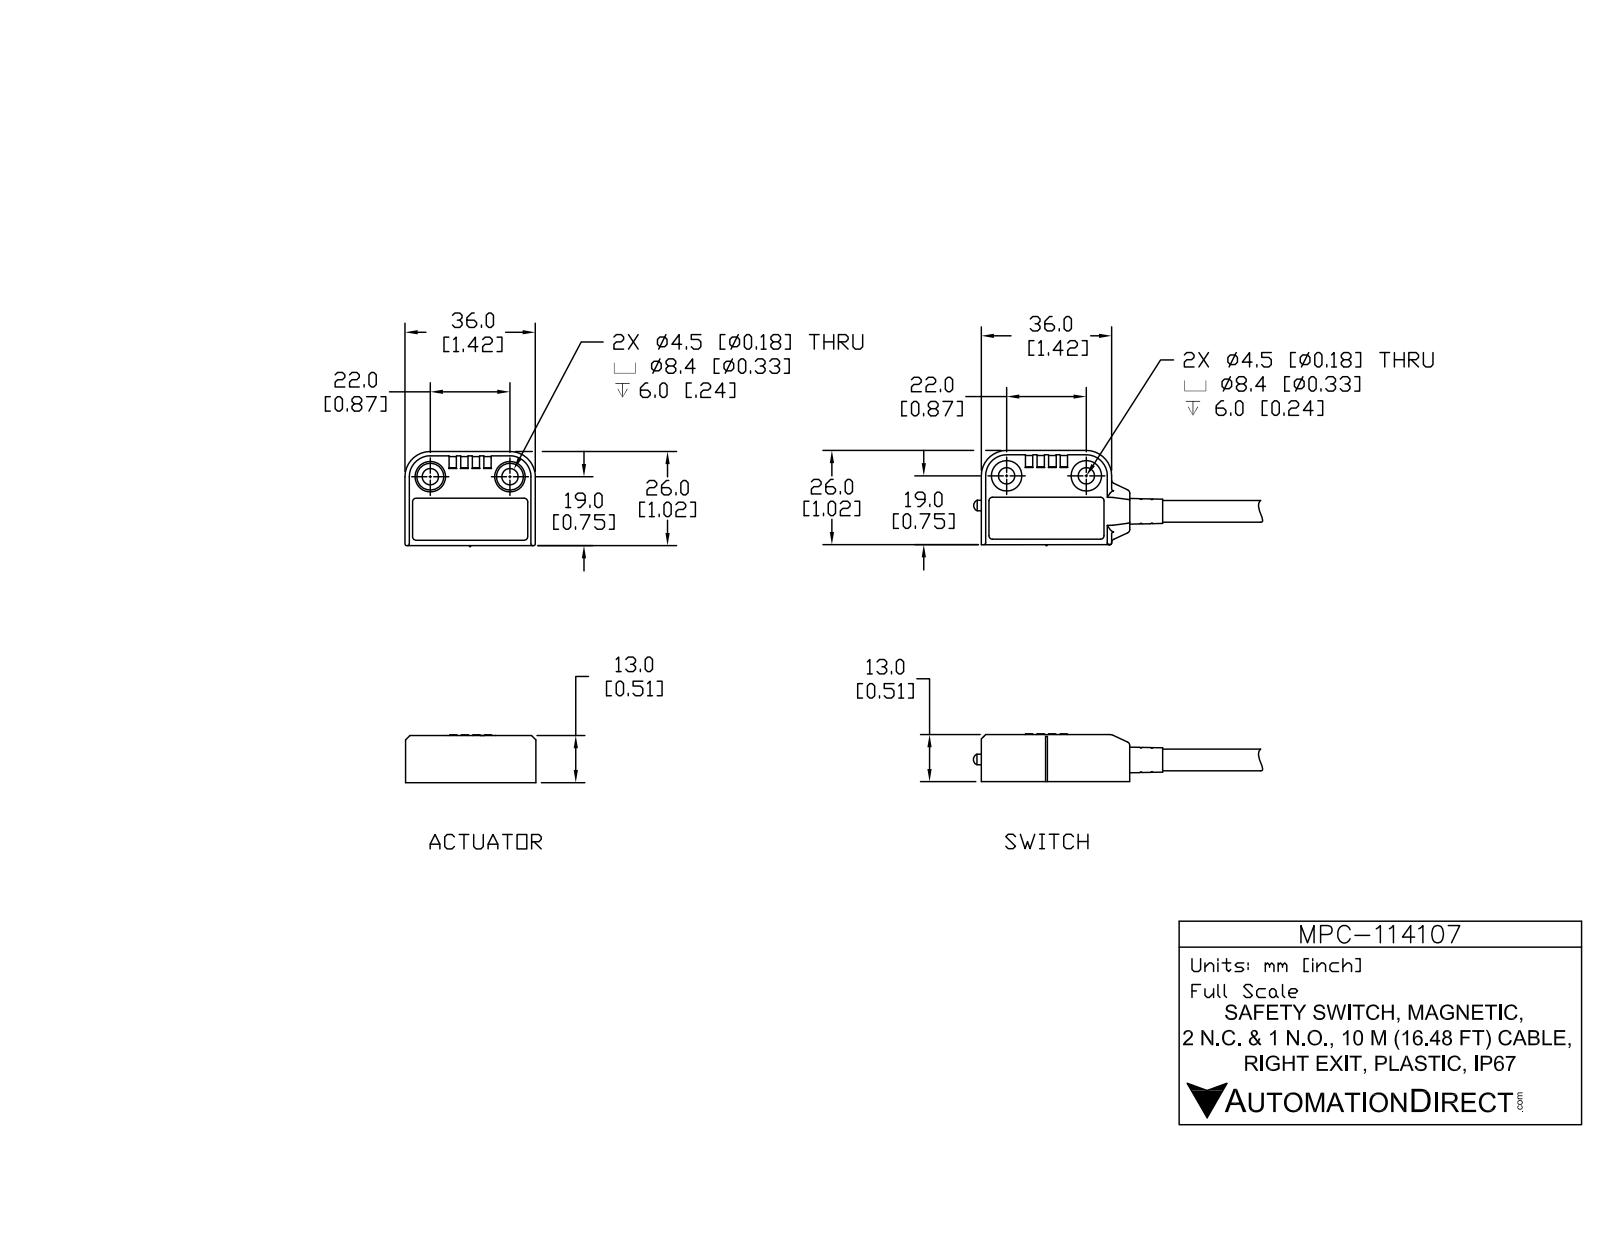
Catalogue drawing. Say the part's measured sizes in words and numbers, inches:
The part is named "MPC-114107_1; MPC-114107_2; MPC-114107". Its 3-D file was written by "SolidWorks 2017 (AUTOMOTIVE_DESIGN)". It is 10 solids with 1072 faces: 453 planar, 349 cylindrical and 270 other. Overall it measures 7.748 by 2.087 by 0.528 inches. Its volume is 1.065 cubic inches and its surface area 29.74 square inches. Round holes: 4 of diameter 0.177, 4 of diameter 0.331, 2 of diameter 0.195, 1 of diameter 0.098, 1 of diameter 0.118, 1 of diameter 0.197, 1 of diameter 0.232, 1 of diameter 0.244, 1 of diameter 0.291. Round bosses or shafts: 2 of diameter 0.236, 2 of diameter 0.197, 2 of diameter 0.091, 2 of diameter 0.079, 2 of diameter 0.031, 1 of diameter 0.339, 1 of diameter 0.299, 1 of diameter 0.28. Partial cylindrical surfaces (rounded edges, fillets, slot ends): 86 of radius 0.02, 35 of radius 0.012, 30 of radius 0.008, 17 of radius 0.004, 13 of radius 0.039, 4 of radius 0.169, 4 of radius 0.201, 4 of radius 0.276. The main face-to-face distances are 0.055, 0.508, 0.449, 0.461, 0.059, 0.047, 1.063, 0.496, 0.445, 0.031. The hole center spacings are 0.866, 0.434, 0.445, 0.974, 1.091, 1.152, 1.393, 1.535.
